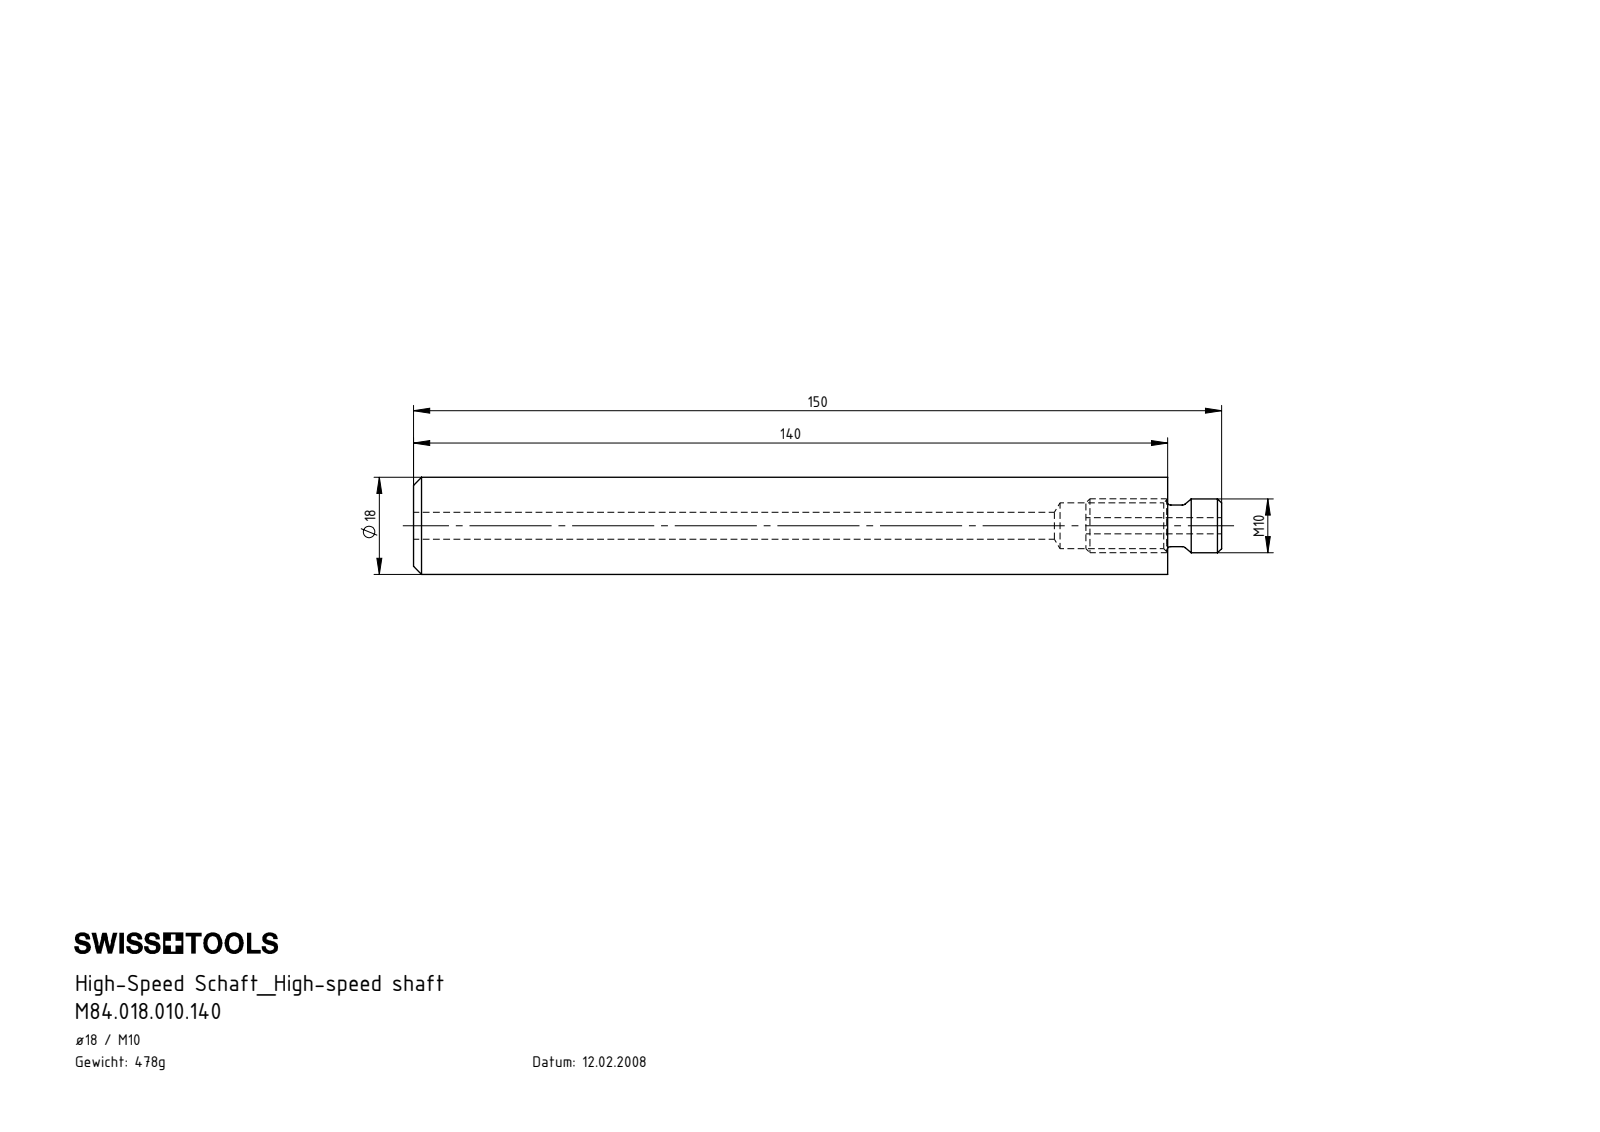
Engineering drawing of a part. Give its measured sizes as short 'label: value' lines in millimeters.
name: HM1-BG1.010.025_A; HM1-U18.001.140_A; M84.018.010.140
written by: SolidWorks 2022 (AUTOMOTIVE_DESIGN)
unit: mm
bodies: 2 solids, 35 faces (5 planar, 14 cylindrical, 16 other)
size: 150 × 18 × 18
volume: 33 712 mm³; area: 11 882 mm²
holes: 1× ⌀3, 1× ⌀5, 1× ⌀8.5
bosses: 1× ⌀18, 1× ⌀10, 1× ⌀7.7
face distances: 140, 150, 10, 124.8, 15.2, 25.2, 139.8, 15, 10.2
